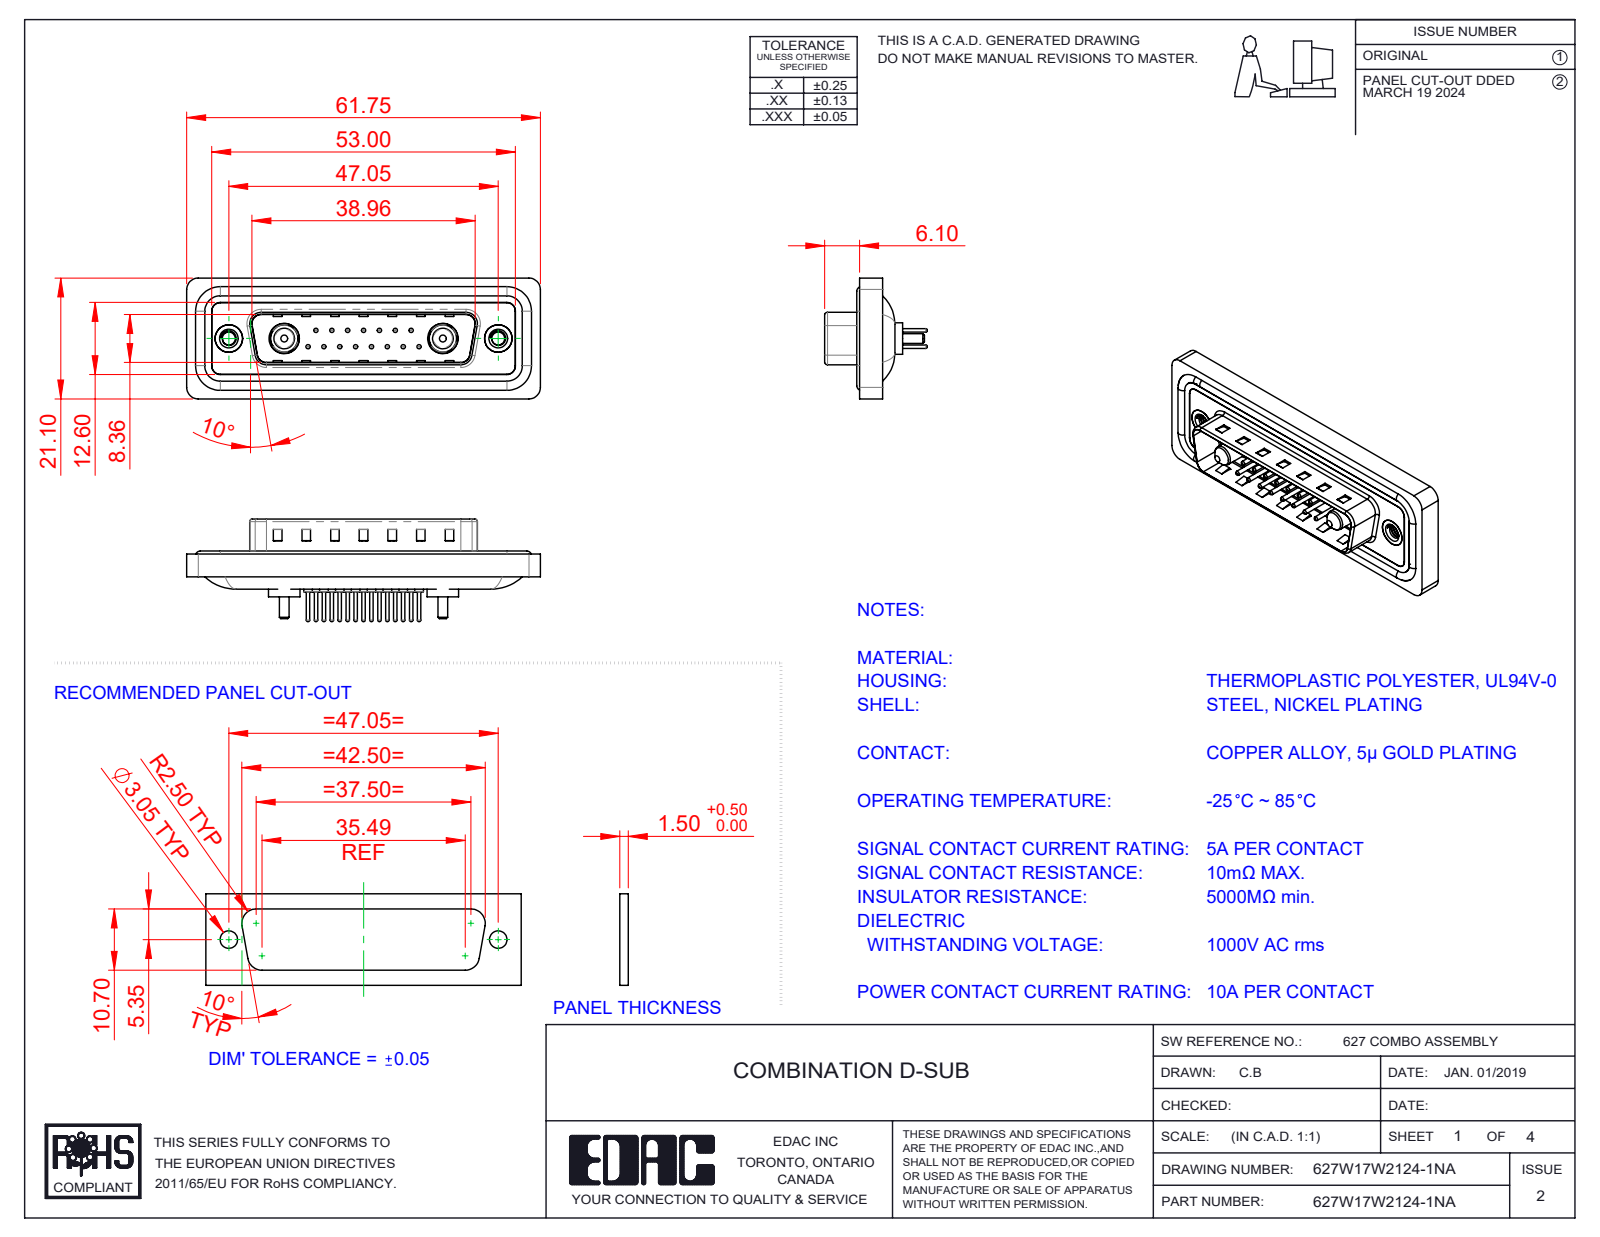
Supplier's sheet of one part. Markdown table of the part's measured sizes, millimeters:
| quantity | value |
| --- | --- |
| part name | 627Combo Shell Front_25 Contacts; Power Pin_10A S; 627Combo Contact Row 1_24; 627Combo Contact Row 2_24 (+5 more) |
| STEP written by | SolidWorks 2023 (CONFIG_CONTROL_DESIGN) |
| units | millimeters |
| bodies | 26 solids, 1114 faces (334 planar, 438 cylindrical, 342 other) |
| overall size | 61.75 × 21.1 × 17.9 |
| volume | 7 239 mm³ |
| surface area | 11 886 mm² |
| round holes (diameter × count) | 0.75 × 15, 1.6 × 15, 2 × 15, 2.26 × 2, 4 × 2, 4.8 × 2, 4.85 × 2, 5 × 2, 5.3 × 2 |
| round bosses / shafts (diameter × count) | 1.5 × 15, 0.6 × 15, 1.6 × 4, 5.5 × 2, 5.2 × 2, 4.9 × 2, 4.75 × 2, 3.75 × 2 |
| partial cylindrical surfaces (radius × count) | 1.5 × 22, 2 × 18, 0.5 × 8, 1.6 × 8, 0.25 × 4, 0.6 × 4, 0.65 × 4, 0.9 × 4 |
| main face-to-face distances | 0.4, 1.5, 1.1, 1.6, 0.5, 3.1, 2.9, 0.82, 9.58, 4.1 |
| hole center spacings | 3.16, 2.77, 5.54, 8.31, 5.04, 7.49, 11.08, 5.03 |
